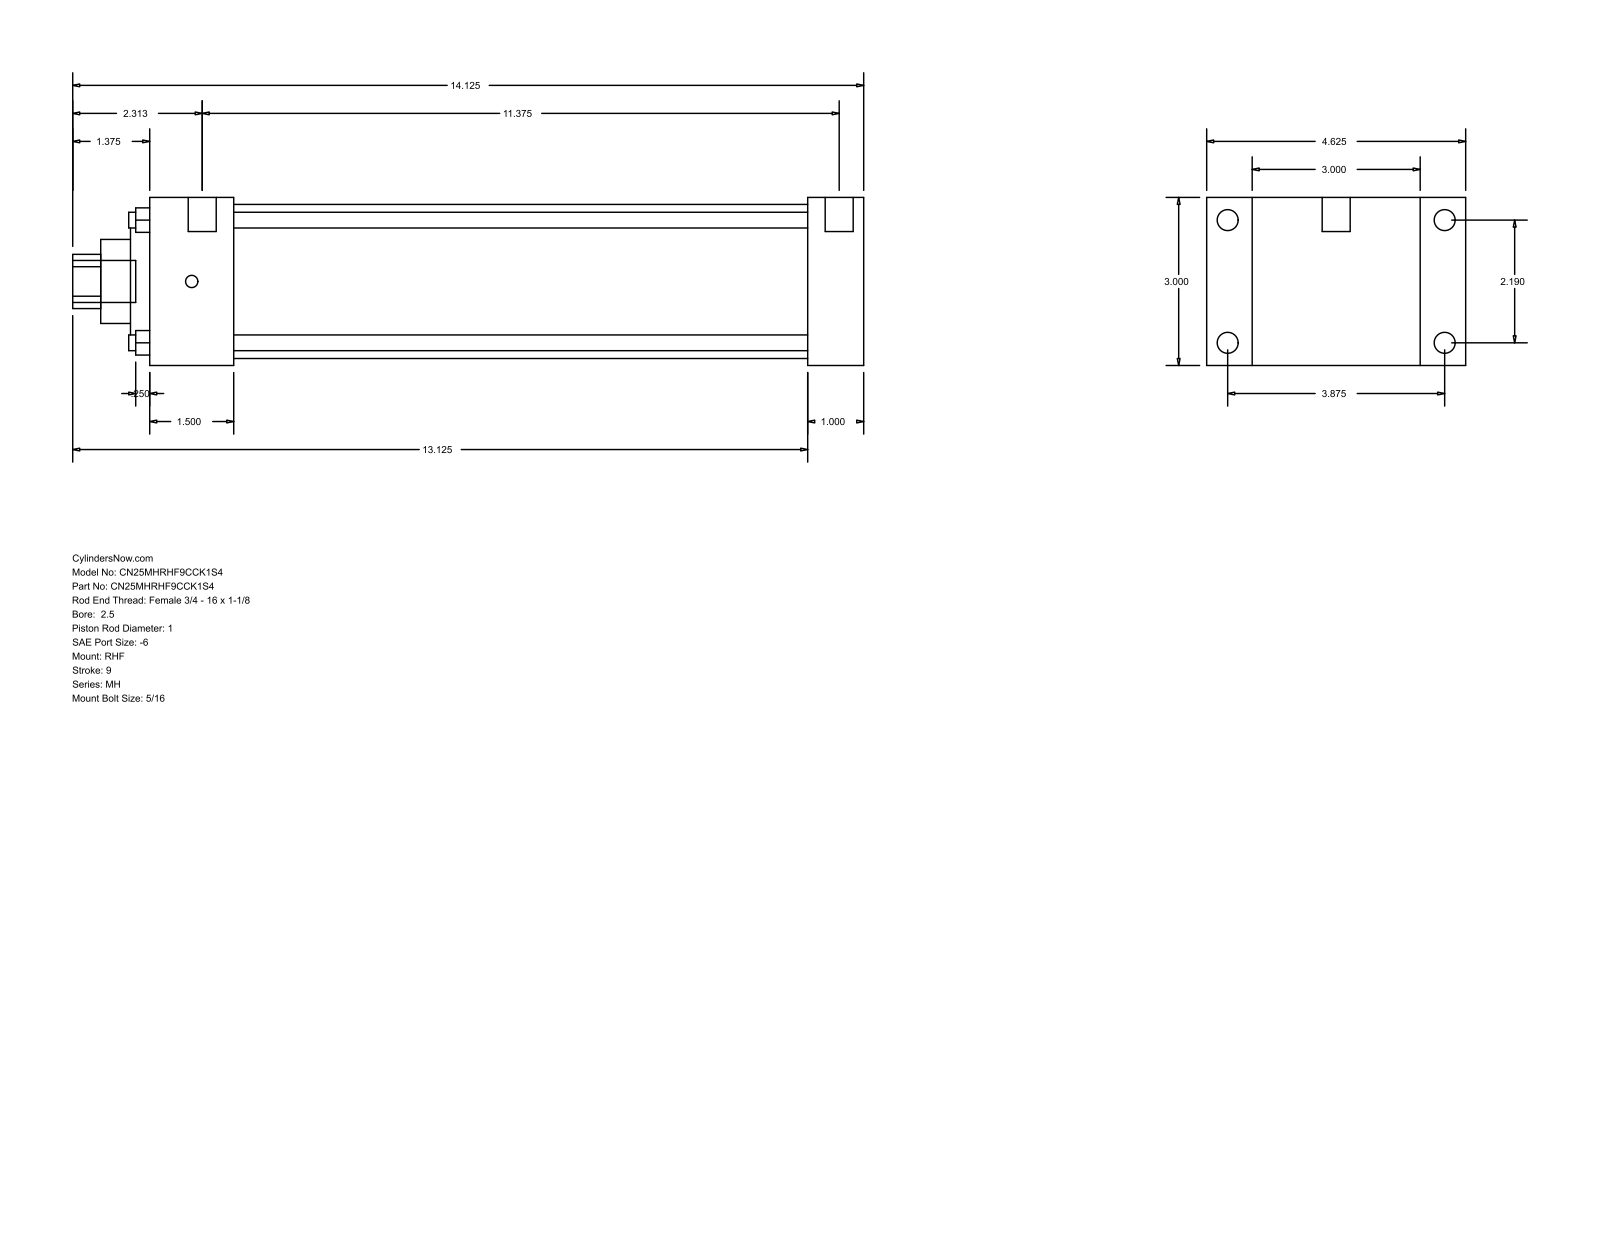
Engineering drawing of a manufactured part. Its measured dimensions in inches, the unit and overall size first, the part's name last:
Units: inches
Overall size (bounding box): 14.125 × 4.625 × 3
Round holes (diameter × count): ⌀0.281 ×4, ⌀1 ×1, ⌀1.5 ×1, ⌀2.375 ×1, ⌀2.75 ×1
Round bosses / shafts (diameter × count): ⌀0.375 ×4, ⌀0.219 ×4, ⌀0.5 ×2, ⌀0.75 ×1
Partial cylindrical surfaces — rounded edges, fillets, slot ends (radius × count): R0.484 ×1
Main face-to-face distances: 3, 1, 0.813, 3.813, 12.75, 11.75, 4.625, 1.5, 10.25, 11.25
Hole centre spacings: 1.548, 2.19, 3.097
Bodies: 0 solids, 90 faces (61 planar, 29 cylindrical, 0 other)
Part name (STEP PRODUCT): MH_RHF__0250_1
STEP written by: GSSL Pune (CONFIG_CONTROL_DESIGN)
